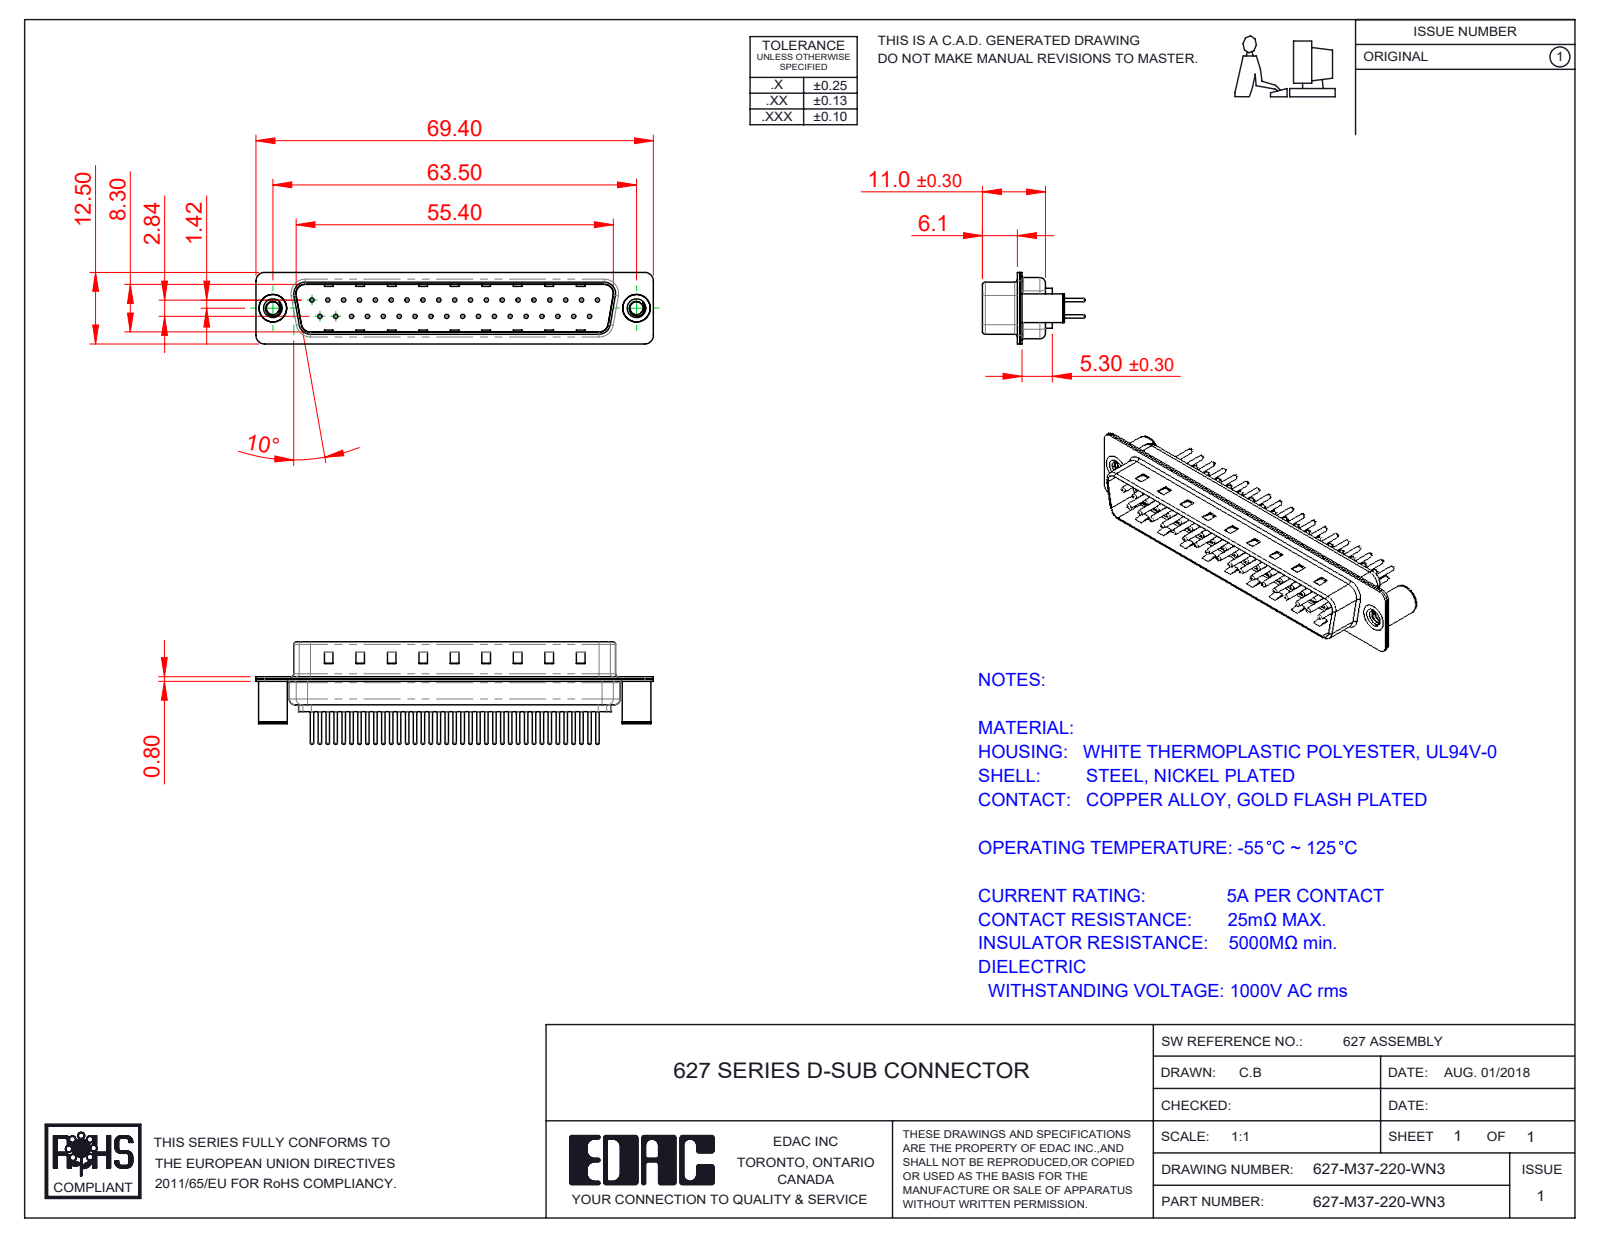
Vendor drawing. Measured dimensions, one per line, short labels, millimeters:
name: 627M Shell Rear_37 Contacts; 627-M37-220-WN3; 627M Contact Row 2_20; 627M Shell Front_37 Contacts (+3 more)
written by: SolidWorks 2020 (CONFIG_CONTROL_DESIGN)
unit: mm
bodies: 42 solids, 1815 faces (462 planar, 683 cylindrical, 670 other)
size: 69.4 × 17.9 × 12.5
volume: 3 891 mm³; area: 9 528 mm²
holes: 37× ⌀0.75, 37× ⌀1.6, 37× ⌀2, 2× ⌀2.26, 2× ⌀3.26, 2× ⌀4, 2× ⌀4.8
bosses: 37× ⌀1.5, 37× ⌀0.6, 2× ⌀5, 2× ⌀4.9
rounds: 16× R1.5, 12× R2, 8× R0.5, 8× R1.6, 4× R0.25, 4× R0.6, 4× R0.65, 4× R0.9
face distances: 0.4, 0.8, 9.5, 9.1, 8.7, 9.9, 1.2, 5.7, 0.75, 0.35
hole spacings: 2.77, 5.54, 3.16, 8.31, 11.08, 13.85, 16.62, 19.39
